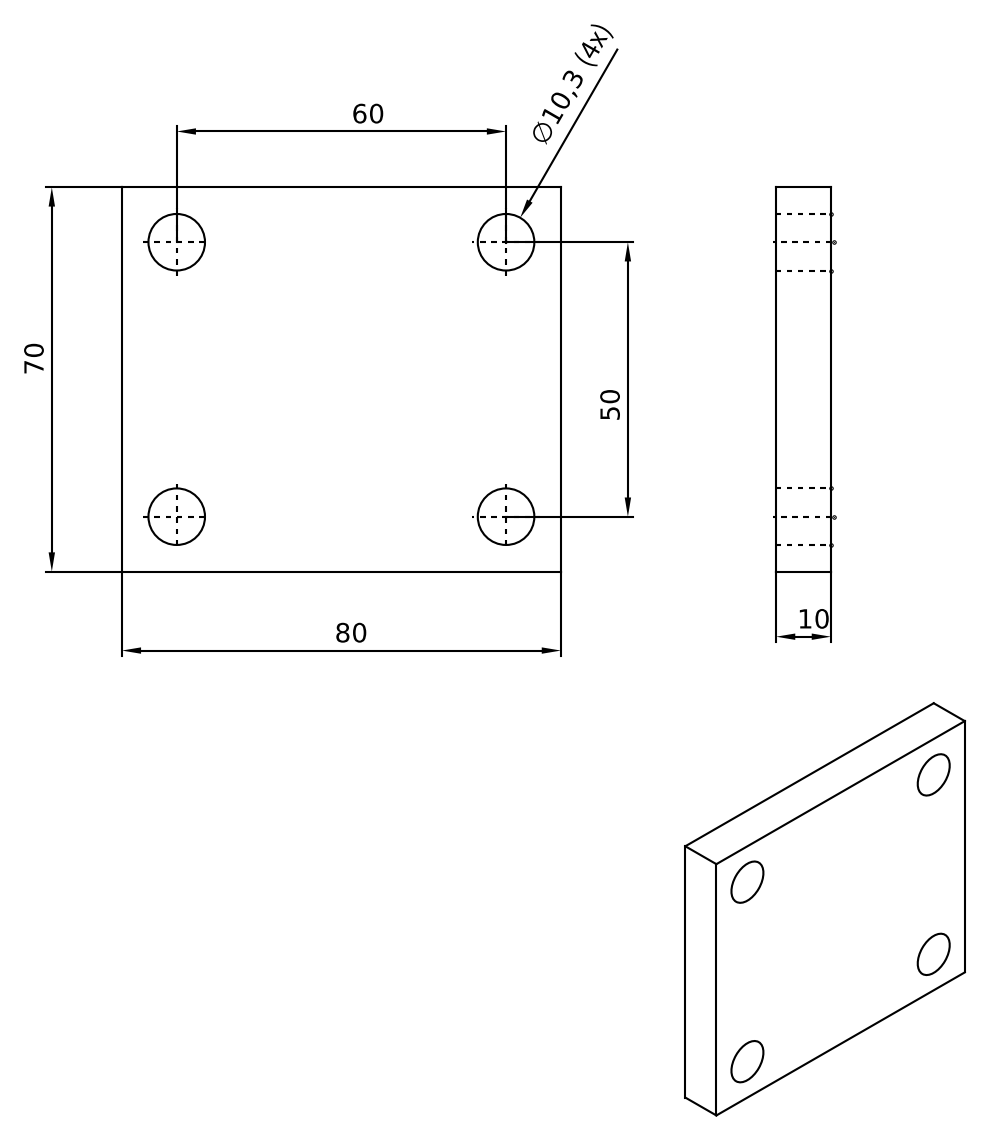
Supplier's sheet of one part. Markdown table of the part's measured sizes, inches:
| quantity | value |
| --- | --- |
| part name | 618-25E1 |
| STEP written by | Autodesk Inventor 8 (AUTOMOTIVE_DESIGN) |
| units | inches |
| bodies | 1 solid, 14 faces (6 planar, 0 cylindrical, 8 other) |
| overall size | 3.15 × 2.756 × 0.394 |
| volume | 3.214 in³ |
| surface area | 22.98 in² |
| main face-to-face distances | 0.394, 2.756, 3.15 |
